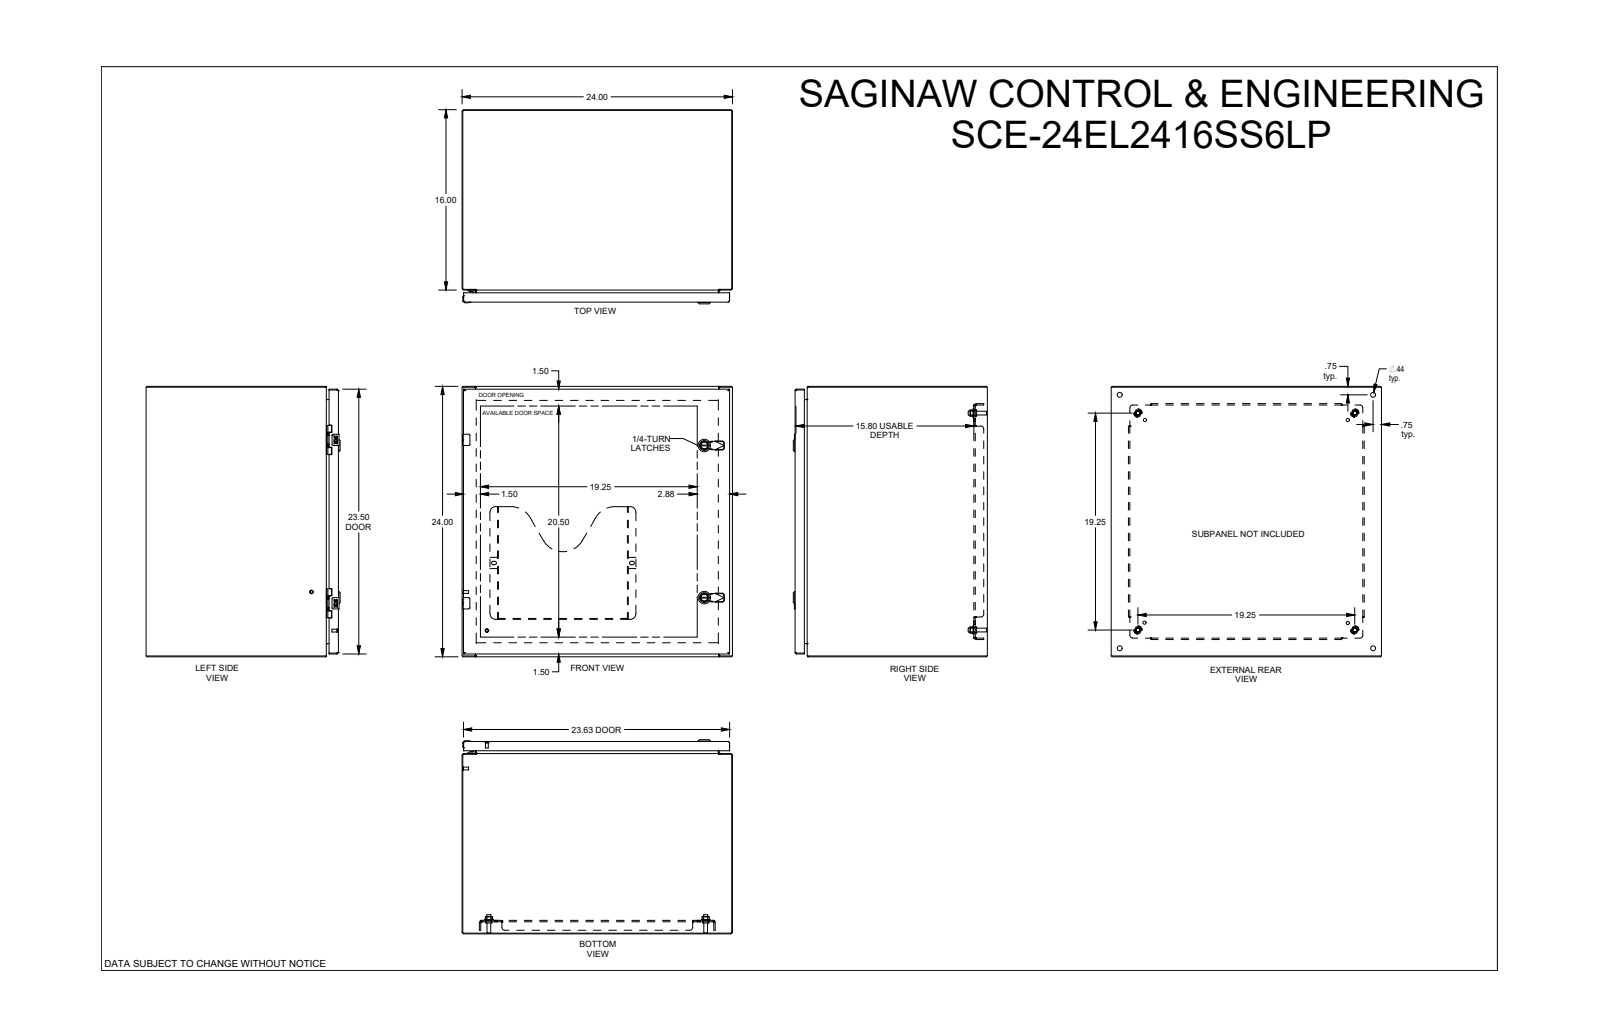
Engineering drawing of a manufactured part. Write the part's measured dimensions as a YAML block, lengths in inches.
part_name: "SCE-24EL2416SS6LP"
step_written_by: "SolidWorks 2019 (CONFIG_CONTROL_DESIGN)"
units: inches
bodies: {solids: 0, faces: 2838, planar: 1307, cylindrical: 759, other: 772}
overall_size: [24, 24, 17.23]
round_holes:
  - {diameter: 0.172, count: 4}
  - {diameter: 0.205, count: 4}
  - {diameter: 0.244, count: 4}
  - {diameter: 0.266, count: 4}
  - {diameter: 0.281, count: 4}
  - {diameter: 0.367, count: 4}
  - {diameter: 0.375, count: 4}
  - {diameter: 0.437, count: 4}
  - {diameter: 0.5, count: 4}
  - {diameter: 0.156, count: 2}
  - {diameter: 0.197, count: 2}
  - {diameter: 0.218, count: 2}
round_bosses_or_shafts:
  - {diameter: 0.17, count: 6}
  - {diameter: 0.366, count: 4}
  - {diameter: 0.332, count: 4}
  - {diameter: 0.25, count: 4}
  - {diameter: 0.248, count: 4}
  - {diameter: 0.196, count: 3}
  - {diameter: 1.102, count: 2}
  - {diameter: 0.866, count: 2}
partial_cylinders:
  - {radius: 0.012, count: 56}
  - {radius: 0.015, count: 32}
  - {radius: 0.01, count: 28}
  - {radius: 0.04, count: 23}
  - {radius: 0.02, count: 20}
  - {radius: 0.029, count: 12}
  - {radius: 0.07, count: 10}
  - {radius: 0.145, count: 10}
face_to_face_distances: [0.075, 23.925, 23.85, 24, 0.075, 16.998, 16.923, 17.073, 16.998, 1.2]
hole_center_spacings: [14.5, 20.938, 0.985, 18.641, 20.38, 0.02, 0.875, 2.298]
